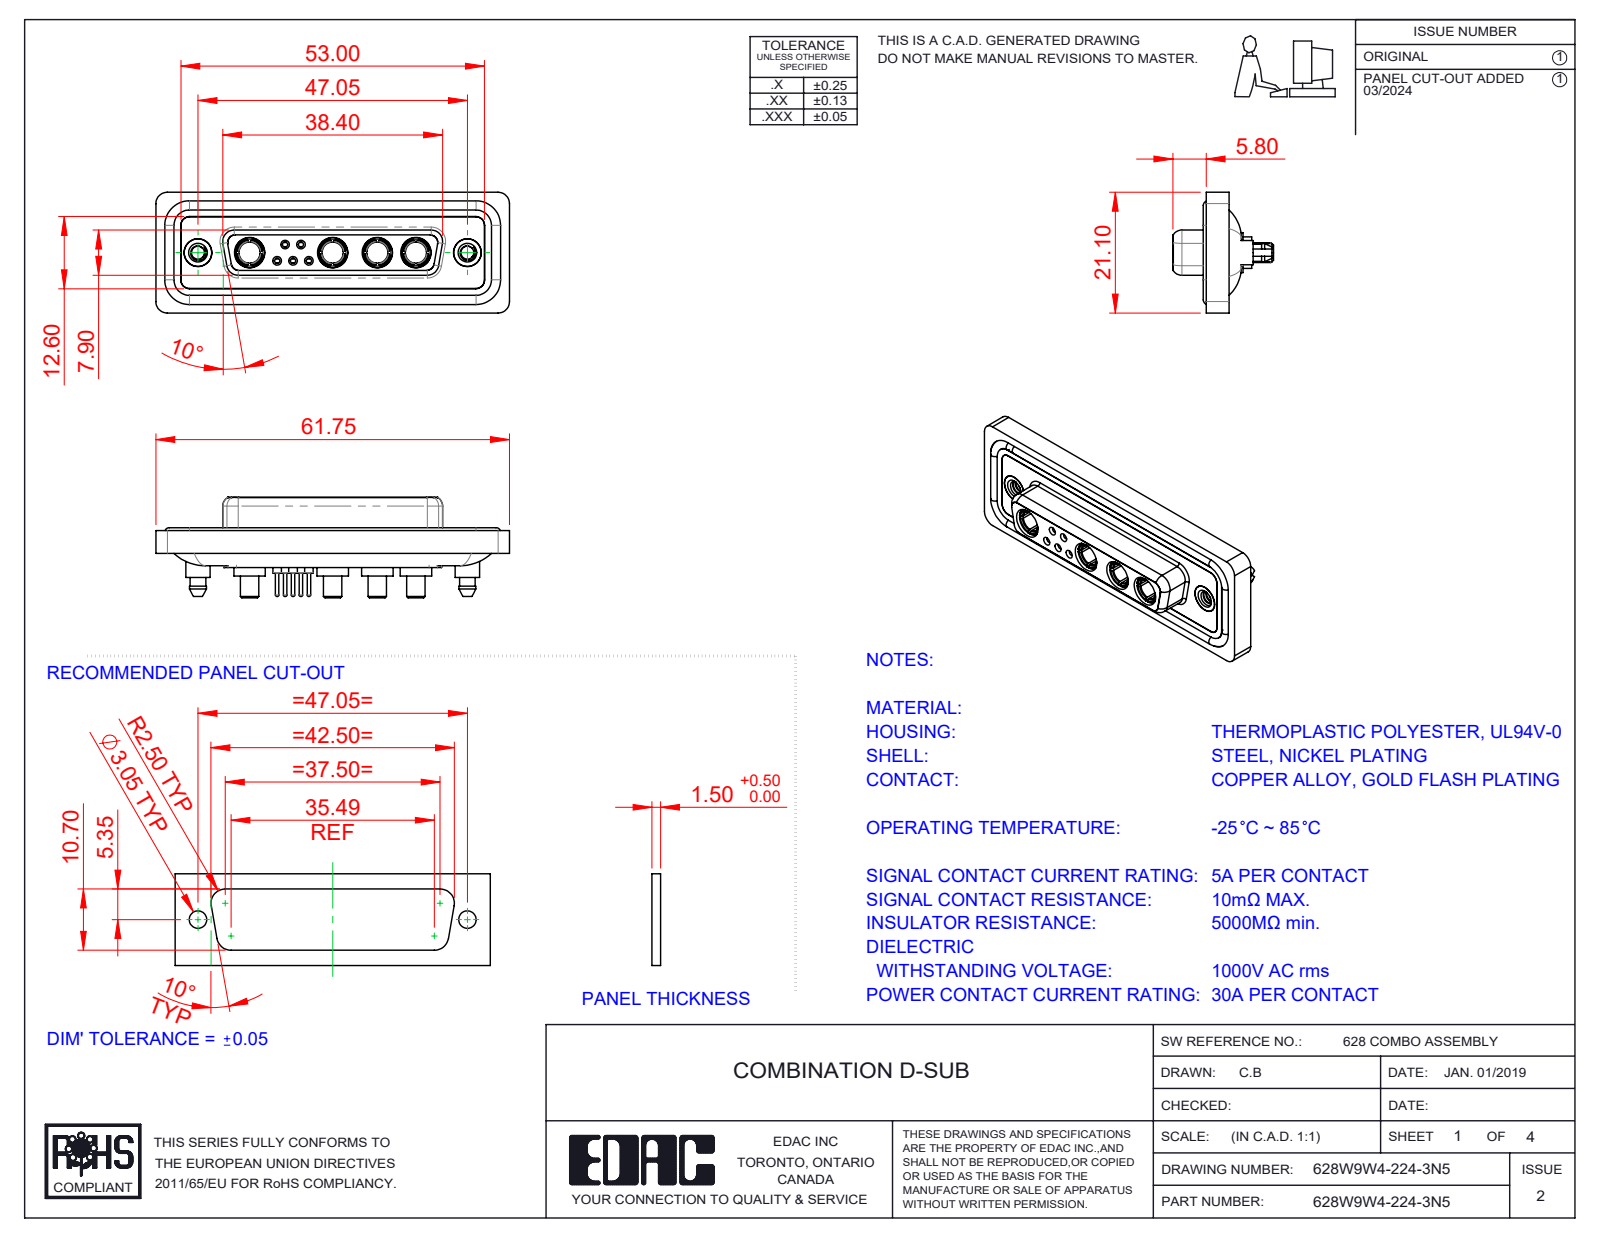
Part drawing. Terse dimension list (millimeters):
name: 628Combo Contact Row 1_24; 628Combo Housing_9W4; 628Combo Shell Front_25 Contacts; 628Combo Threaded Boardlock_5 (+5 more)
written by: SolidWorks 2023 (CONFIG_CONTROL_DESIGN)
unit: mm
bodies: 20 solids, 1007 faces (312 planar, 407 cylindrical, 288 other)
size: 61.75 × 21.1 × 17.55
volume: 8 385 mm³; area: 13 913 mm²
holes: 6× ⌀4.85, 5× ⌀0.9, 5× ⌀1.1, 5× ⌀1.5, 5× ⌀2, 4× ⌀3.7, 4× ⌀5.3, 3× ⌀1.6, 2× ⌀1.7, 2× ⌀2.26, 2× ⌀4, 2× ⌀4.05
bosses: 6× ⌀1.6, 5× ⌀2.2, 5× ⌀0.6, 4× ⌀5.5, 4× ⌀5.2, 4× ⌀4.96, 4× ⌀4.75, 4× ⌀3.75
rounds: 24× R1.5, 18× R2, 10× R1.6, 8× R1.35, 4× R0.25, 4× R0.5, 4× R0.6, 4× R0.65
face distances: 0.4, 1.8, 7.45, 5.65, 0.5, 7.05, 6.6, 1.6, 1.1, 2.9
hole spacings: 3.16, 2.77, 5.03, 2.76, 4.4, 5.02, 5.54, 5.73
